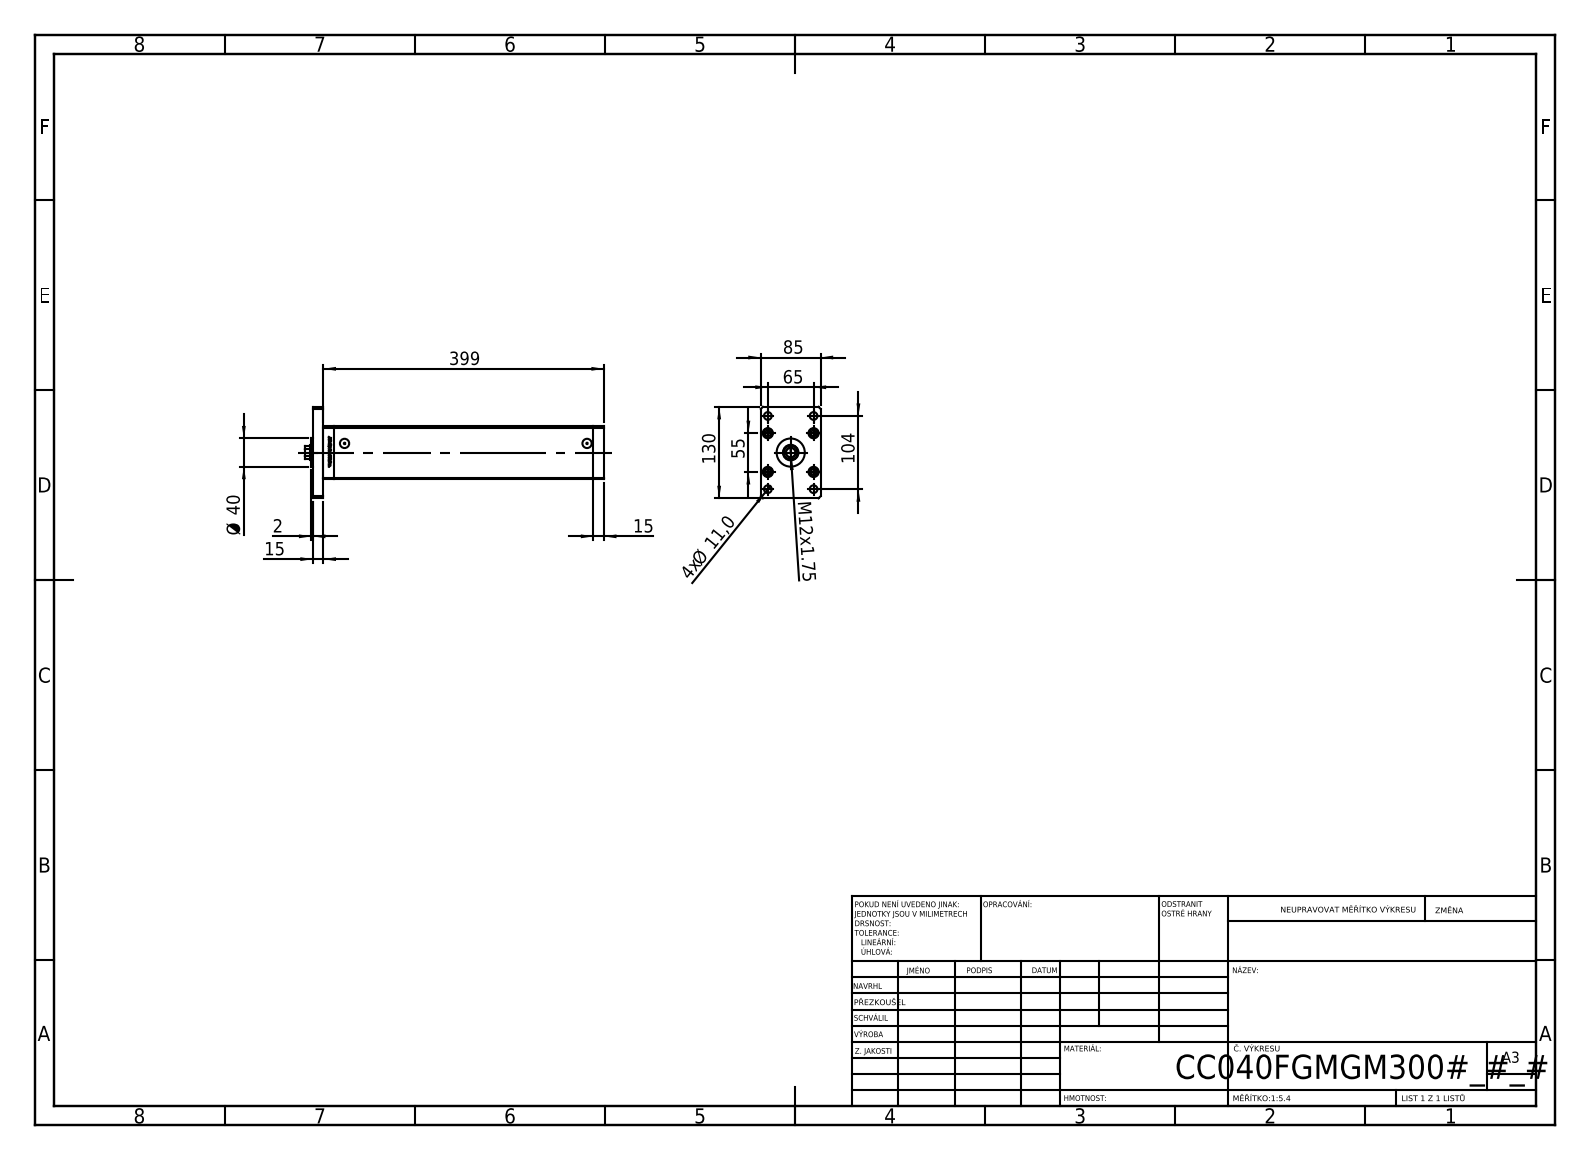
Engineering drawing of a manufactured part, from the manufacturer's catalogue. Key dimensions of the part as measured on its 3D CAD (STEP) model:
Part name (STEP PRODUCT): V220C_F_MIDDLE; V220C_VC_F; V220C_FRONT_F; V220C BACK_F (+2 more)
STEP written by: SolidWorks 2019 (CONFIG_CONTROL_DESIGN)
Units: millimetres
Bodies: 19 solids, 1308 faces (515 planar, 187 cylindrical, 606 other)
Overall size (bounding box): 425 × 130 × 85
Volume: 2 331 000 mm³ · Surface area: 316 415 mm²
Round holes (diameter × count): ⌀11 ×9, ⌀15.5 ×5, ⌀10 ×4, ⌀14.5 ×4, ⌀2 ×2, ⌀13.16 ×2, ⌀13.5 ×1, ⌀22 ×1, ⌀23.5 ×1
Round bosses / shafts (diameter × count): ⌀8 ×9, ⌀14.5 ×5, ⌀40 ×1
Partial cylindrical surfaces — rounded edges, fillets, slot ends (radius × count): R0.93 ×2, R10.5 ×1
Main face-to-face distances: 85, 15, 75, 383.5, 398.5, 368.5, 30, 10.5, 413.5, 64.5
Hole centre spacings: 28, 24.5, 42.57, 61.32, 65, 69.46, 79.5, 102.69
